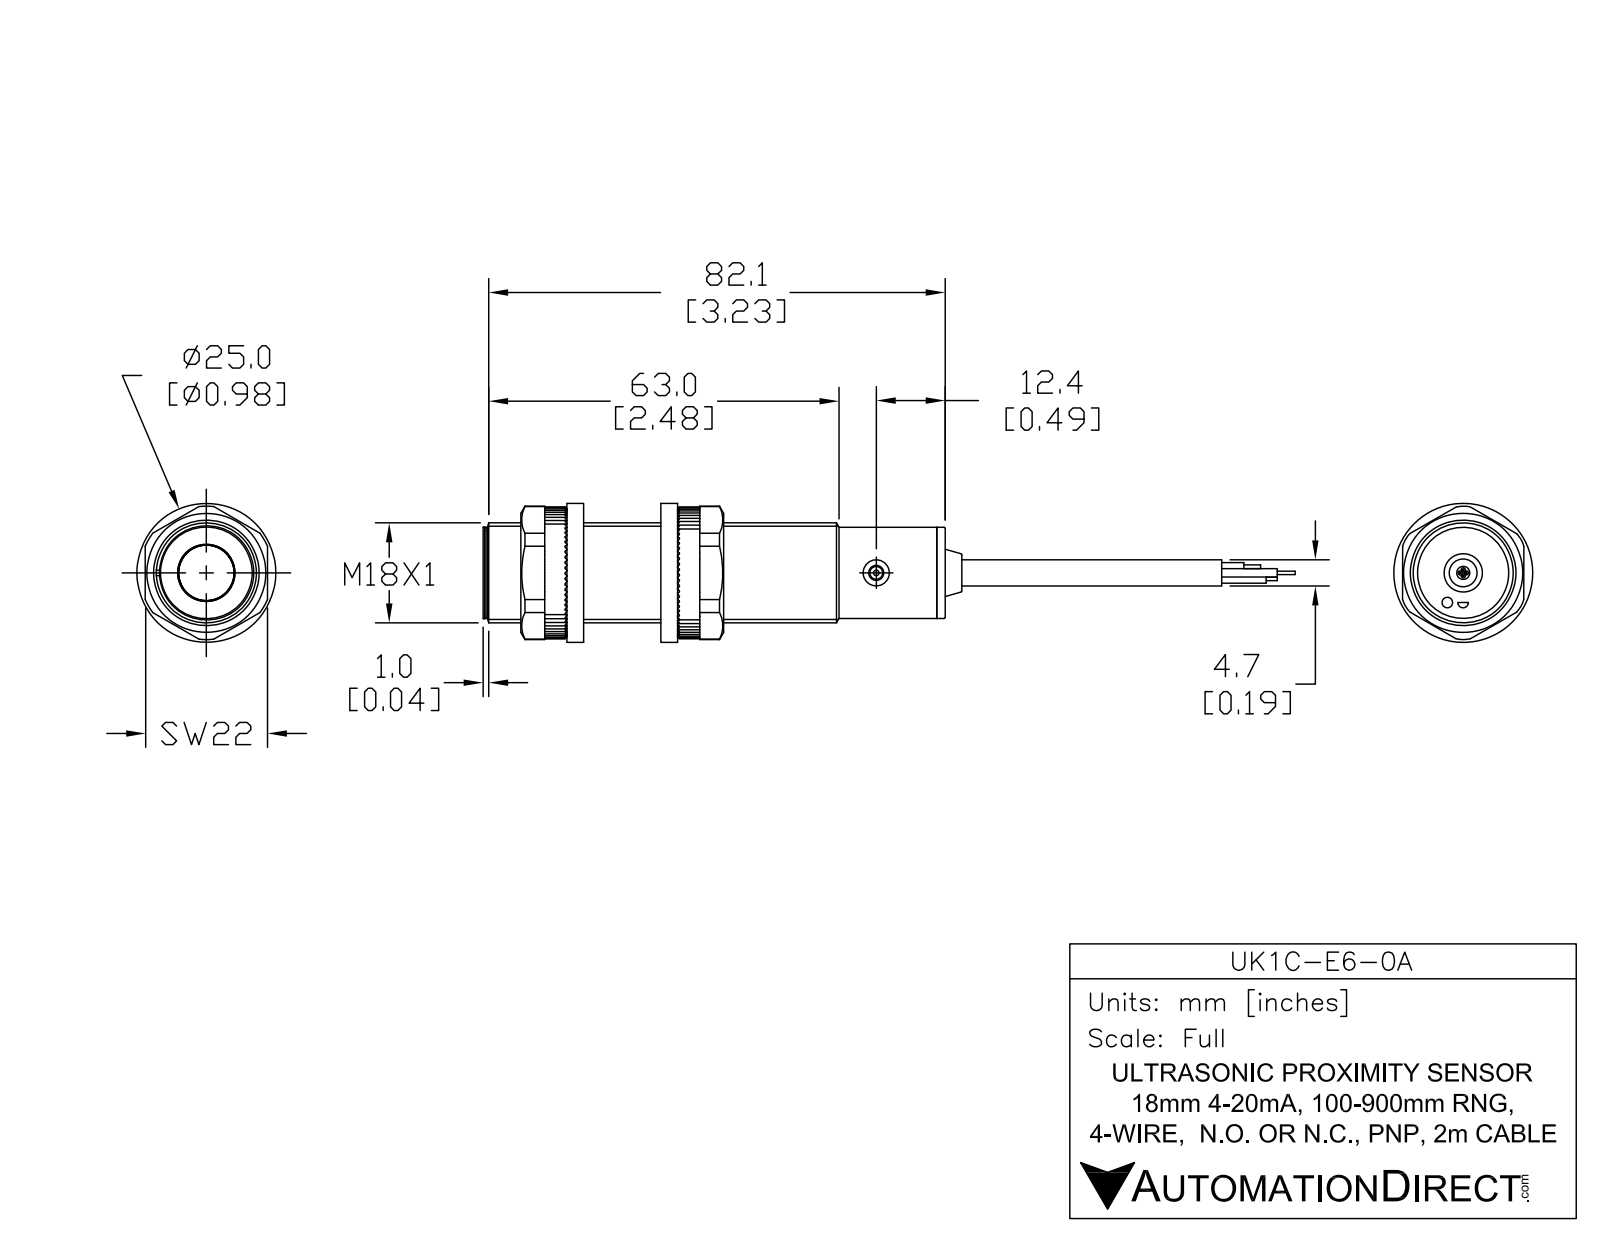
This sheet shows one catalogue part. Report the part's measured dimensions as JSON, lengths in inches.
{"part_name": "UK1C-E6-0A", "step_written_by": "SolidWorks 2017 (AUTOMOTIVE_DESIGN)", "units": "inches", "bodies": {"solids": 6, "faces": 55, "planar": 17, "cylindrical": 24, "other": 14}, "overall_size": [4.832, 0.709, 0.709], "volume_in3": 1.285, "surface_area_in2": 10.69, "round_holes": [[0.185, 2], [0.106, 1]], "round_bosses_or_shafts": [[0.709, 1], [0.646, 1], [0.622, 1], [0.374, 1], [0.189, 1], [0.091, 1]], "face_to_face_distances": [3.193, 3.252, 0.059, 0.039, 3.232, 3.291, 0.041, 3.234, 3.293, 3.257]}
